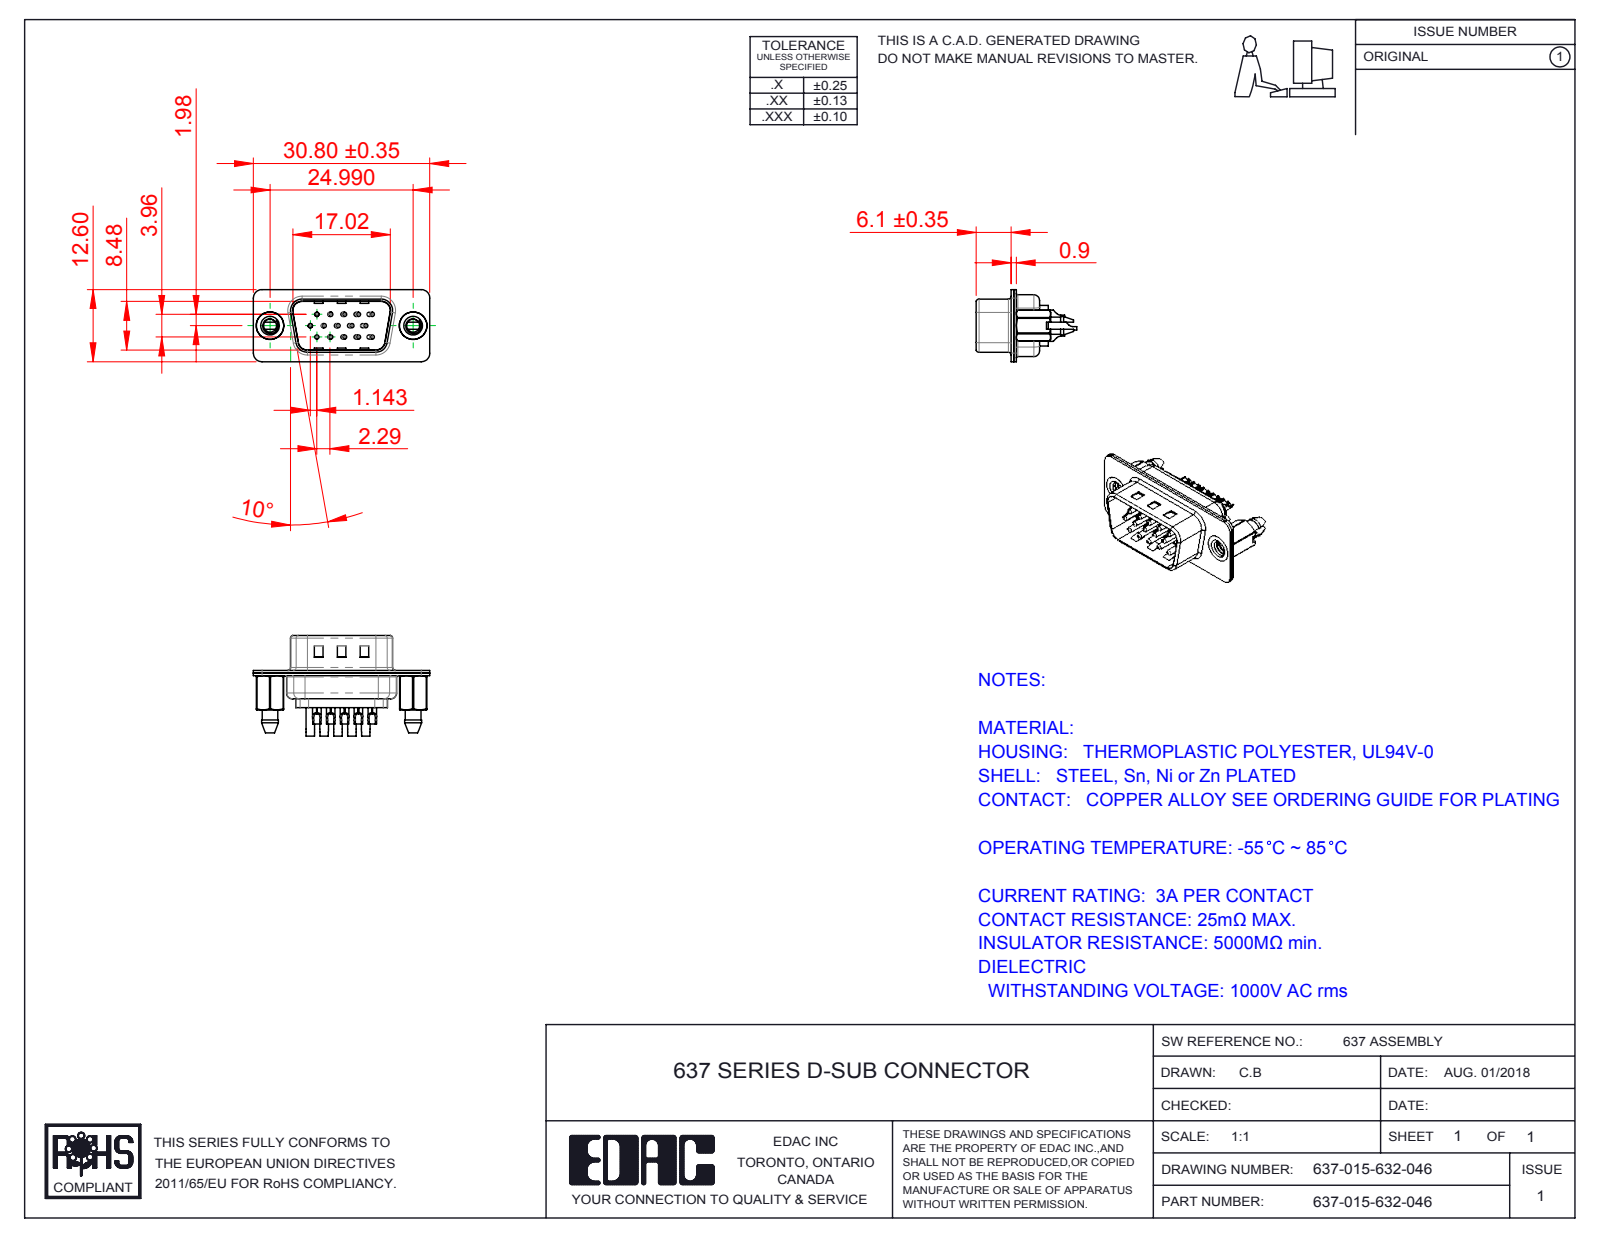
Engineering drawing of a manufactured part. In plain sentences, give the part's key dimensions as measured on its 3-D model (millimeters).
The part is named "637-015-632-046; 637 4-40 Threaded Boardlock_LP; 637 Contact Row 3_32; 637 Contact Row 1_32 (+4 more)". Its 3-D file was written by "SolidWorks 2016 (CONFIG_CONTROL_DESIGN)". It is 20 solids with 1338 faces: 349 planar, 596 cylindrical and 393 other. Overall it measures 30.8 by 17.55 by 12.6 millimeters. Its volume is 1 444 cubic millimeters and its surface area 5 064 square millimeters. Round holes: 27 of diameter 1.6, 15 of diameter 0.35, 15 of diameter 1.1, 12 of diameter 0.75, 12 of diameter 2, 2 of diameter 2.26, 2 of diameter 4, 2 of diameter 4.8. Round bosses or shafts: 15 of diameter 2, 15 of diameter 1.5, 15 of diameter 0.75, 2 of diameter 4.9. Partial cylindrical surfaces (rounded edges, fillets, slot ends): 18 of radius 1.5, 12 of radius 2, 8 of radius 0.5, 7 of radius 1, 6 of radius 1.6, 4 of radius 0.25, 4 of radius 0.55, 4 of radius 0.7. The main face-to-face distances are 0.45, 0.4, 0.9, 0.7, 8.48, 8.88, 6.5, 4.55, 0.31, 1.95. The hole center spacings are 3.96, 2.29, 2.28, 4.57, 2.42, 6.05, 4.84, 2.35.
